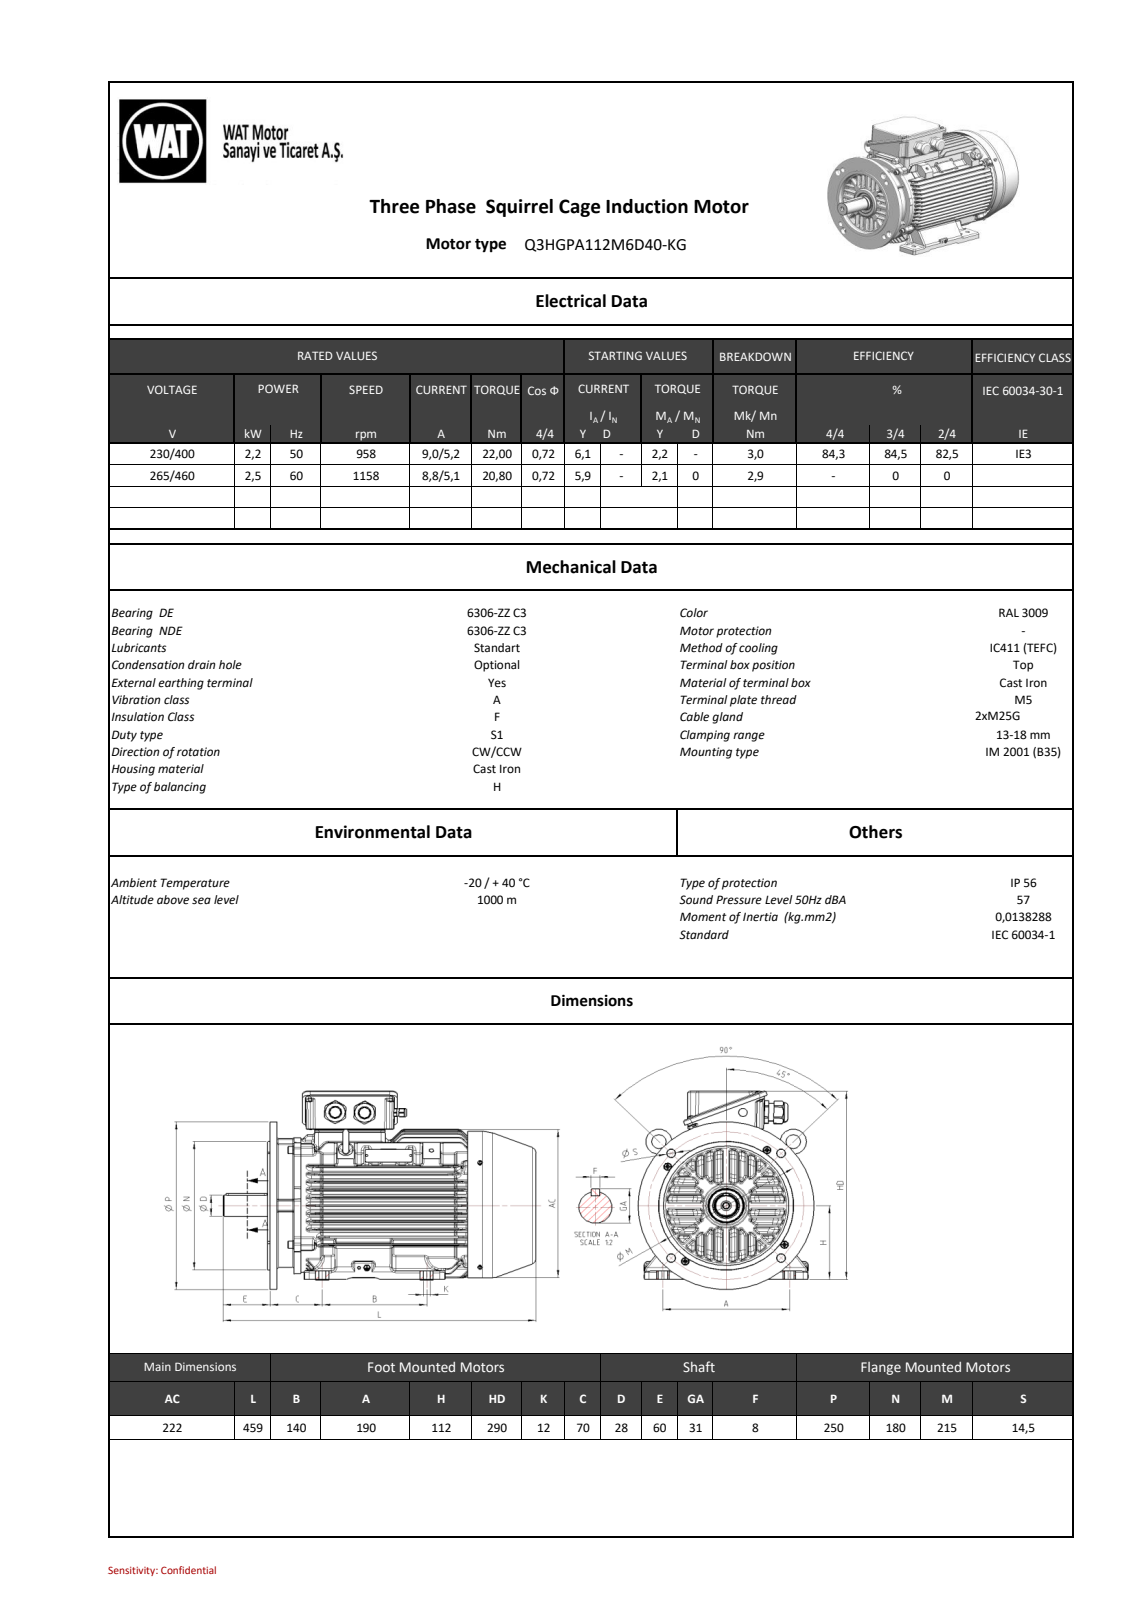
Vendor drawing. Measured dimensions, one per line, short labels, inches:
name: 26000A30F4D8rolw
written by: SIEMENS PLM Software NX 11.0 (AUTOMOTIVE_DESIGN)
unit: in
bodies: 0 solids, 5273 faces (974 planar, 1546 cylindrical, 2753 other)
size: 18.051 × 11.925 × 9.843
holes: 9× ⌀0.197, 6× ⌀0.177, 4× ⌀0.512, 2× ⌀0.098, 2× ⌀0.13, 2× ⌀0.268, 2× ⌀0.276, 2× ⌀0.394, 2× ⌀0.677, 1× ⌀0.138, 1× ⌀0.315, 1× ⌀0.413
bosses: 2× ⌀1.091, 2× ⌀0.994, 2× ⌀0.787, 1× ⌀9.843, 1× ⌀8.465, 1× ⌀7.559, 1× ⌀7.087, 1× ⌀1.575
rounds: 284× R0.157, 156× R0.118, 115× R0.02, 114× R0.059, 49× R0.197, 29× R0.079, 25× R0.039, 25× R0.071
face distances: 0.516, 1.035, 0.519, 1.573, 3.565, 1.557, 1.041, 0.522, 3.046, 2.53
hole spacings: 3.819, 4.528, 5.401, 1.326, 4.041, 4.381, 6.069, 6.257
